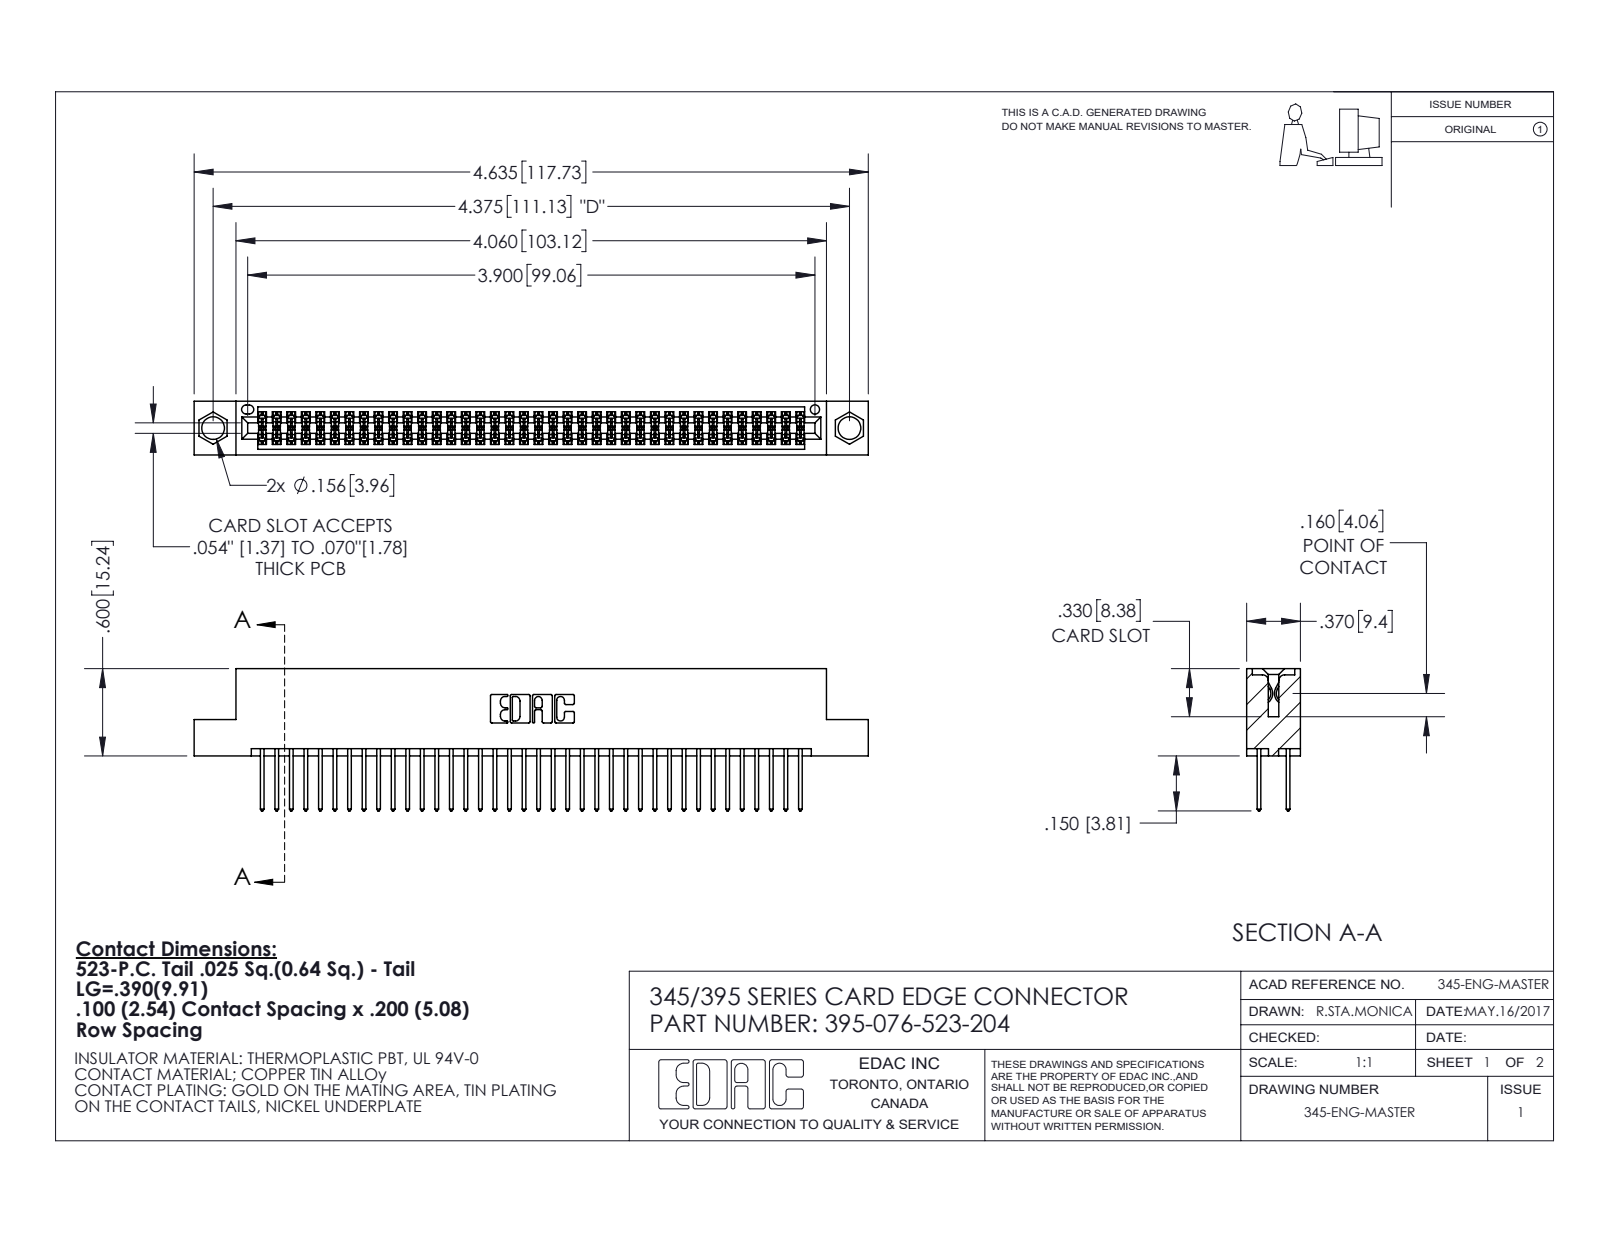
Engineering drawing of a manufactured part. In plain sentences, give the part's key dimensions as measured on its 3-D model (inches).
The part is named "395-076-523-204; 345-292-001_345-293-123; 345 Part_Flush Mounting Lugs - 0.156 Dia-TI". Its 3-D file was written by "SolidWorks 2020 (CONFIG_CONTROL_DESIGN)". It is 77 solids with 3940 faces: 2602 planar, 1338 cylindrical and 0 other. Overall it measures 4.635 by 0.977 by 0.37 inches. Its volume is 0.699 cubic inches and its surface area 26.96 square inches. Round holes: 2 of diameter 0.156, 1 of diameter 0.064. Partial cylindrical surfaces (rounded edges, fillets, slot ends): 152 of radius 0.006, 76 of radius 0.01, 22 of radius 0.01, 6 of radius 0.007, 6 of radius 0.031, 3 of radius 0.026, 2 of radius 0.014, 2 of radius 0.019. The main face-to-face distances are 0.072, 0.298, 0.2, 0.098, 0.272, 0.025, 0.37, 0.225, 0.175, 0.149. The hole center spacings are 0.27, 4.139, 4.375.
